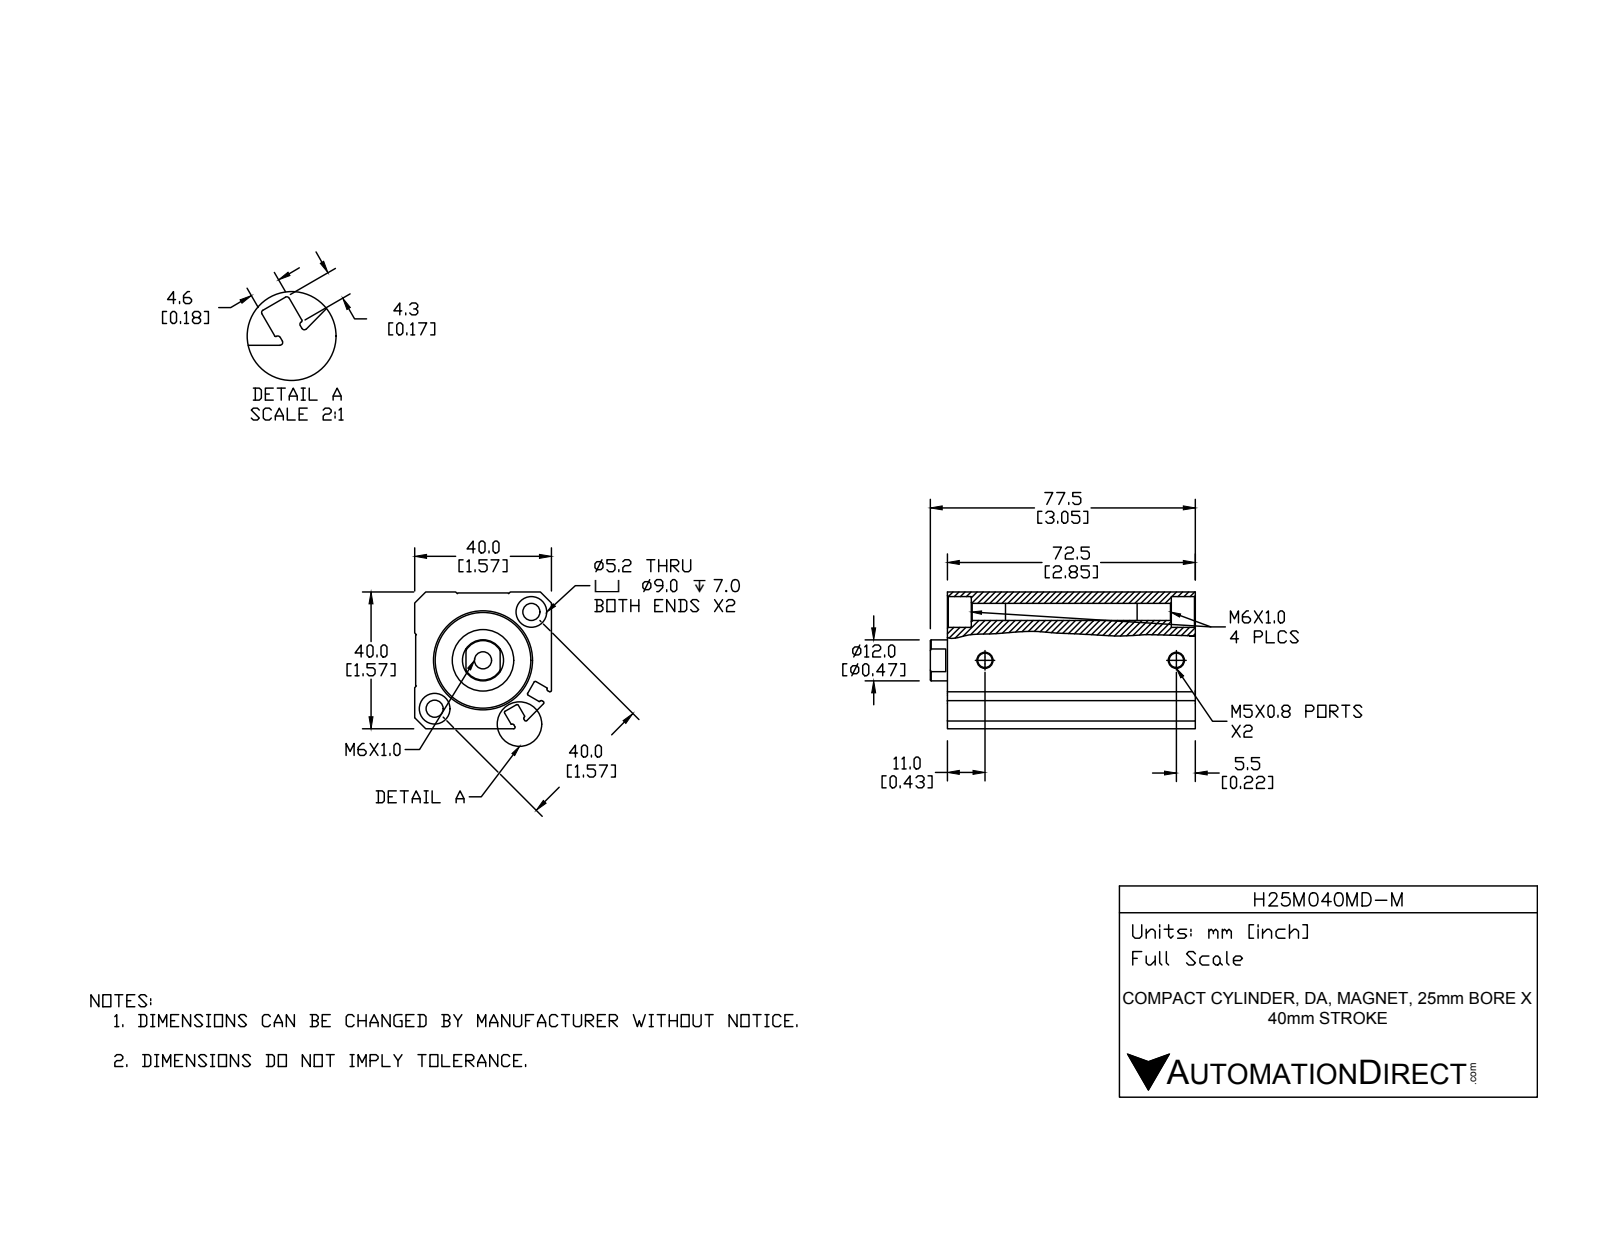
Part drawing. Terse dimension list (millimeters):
name: H25M040MD-M-PISTON; H25M040MD-M-BODY; H25M040MD-M
written by: SolidWorks 2015 (CONFIG_CONTROL_DESIGN)
unit: mm
bodies: 2 solids, 141 faces (53 planar, 55 cylindrical, 33 other)
size: 77.5 × 40 × 40
volume: 85 774 mm³; area: 29 070 mm²
holes: 3× ⌀5, 2× ⌀4.2, 2× ⌀9, 1× ⌀12, 1× ⌀16, 1× ⌀25, 1× ⌀28
bosses: 1× ⌀18, 1× ⌀14
rounds: 12× R0.4, 4× R0.2
face distances: 40, 39.7, 4, 72.5, 68.5, 4.6, 1.4, 2.6, 71.1, 61.5
hole spacings: 20, 39.99, 56
